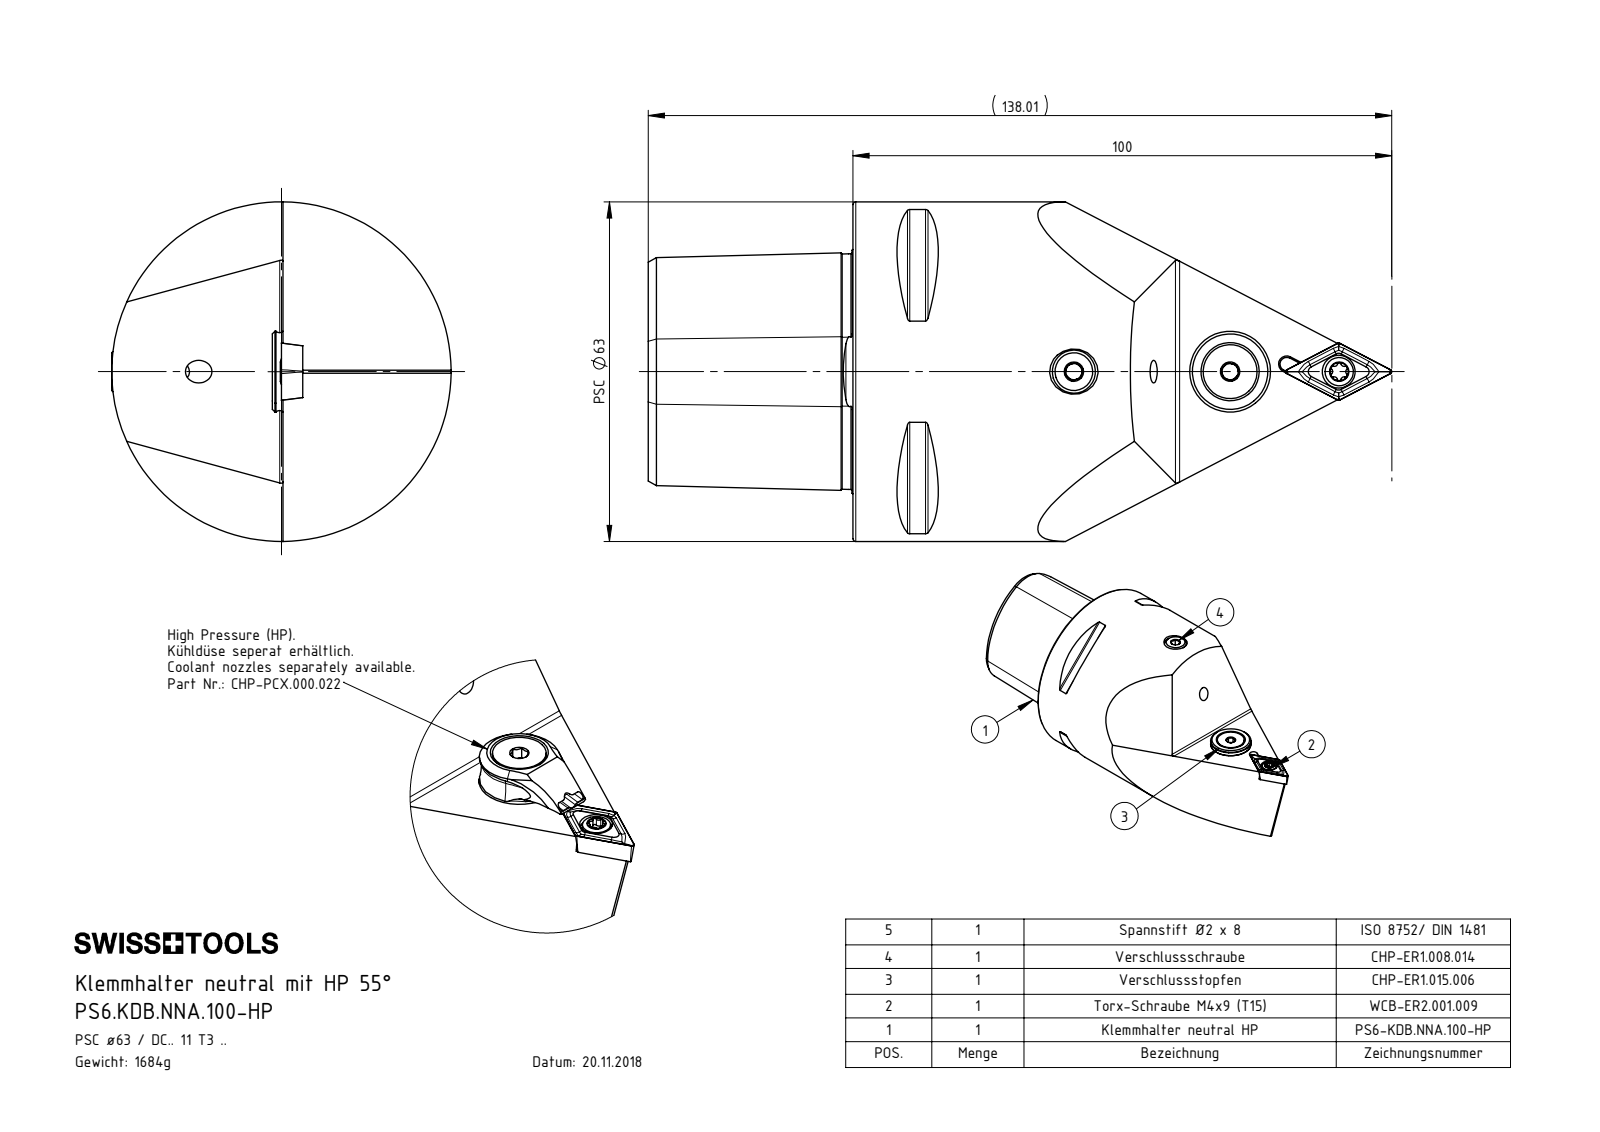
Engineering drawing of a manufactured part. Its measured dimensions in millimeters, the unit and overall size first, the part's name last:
Units: millimetres
Overall size (bounding box): 138.01 × 63 × 63
Round holes (diameter × count): ⌀4.2 ×3, ⌀1.2 ×1, ⌀2 ×1, ⌀2.5 ×1, ⌀3 ×1, ⌀3.3 ×1, ⌀4 ×1, ⌀4.4 ×1, ⌀5 ×1, ⌀5.2 ×1, ⌀6.1 ×1, ⌀7 ×1
Round bosses / shafts (diameter × count): ⌀63 ×1, ⌀15 ×1, ⌀13.4 ×1, ⌀10 ×1, ⌀8 ×1, ⌀5.5 ×1, ⌀5.25 ×1, ⌀5 ×1
Partial cylindrical surfaces — rounded edges, fillets, slot ends (radius × count): R0.5 ×10, R0.34 ×6, R0.59 ×6, R1.25 ×1, R6 ×1, R7 ×1
Main face-to-face distances: 55, 38, 93, 24.88, 4.5, 27, 11, 66, 55.8, 0.83
Hole centre spacings: 4.5, 16.72, 16.82, 20.09, 20.19, 27.5, 58.11, 61.37
Volume: 214 603 mm³ · Surface area: 34 308 mm²
Bodies: 8 solids, 375 faces (89 planar, 98 cylindrical, 188 other)
Part name (STEP PRODUCT): CHP-ER1.008.014_A; CHP-ER1.015.006; CHP-ER1.015.006_A; DIN 7991 - M5x15 (+6 more)
STEP written by: SolidWorks 2017 (AUTOMOTIVE_DESIGN)
